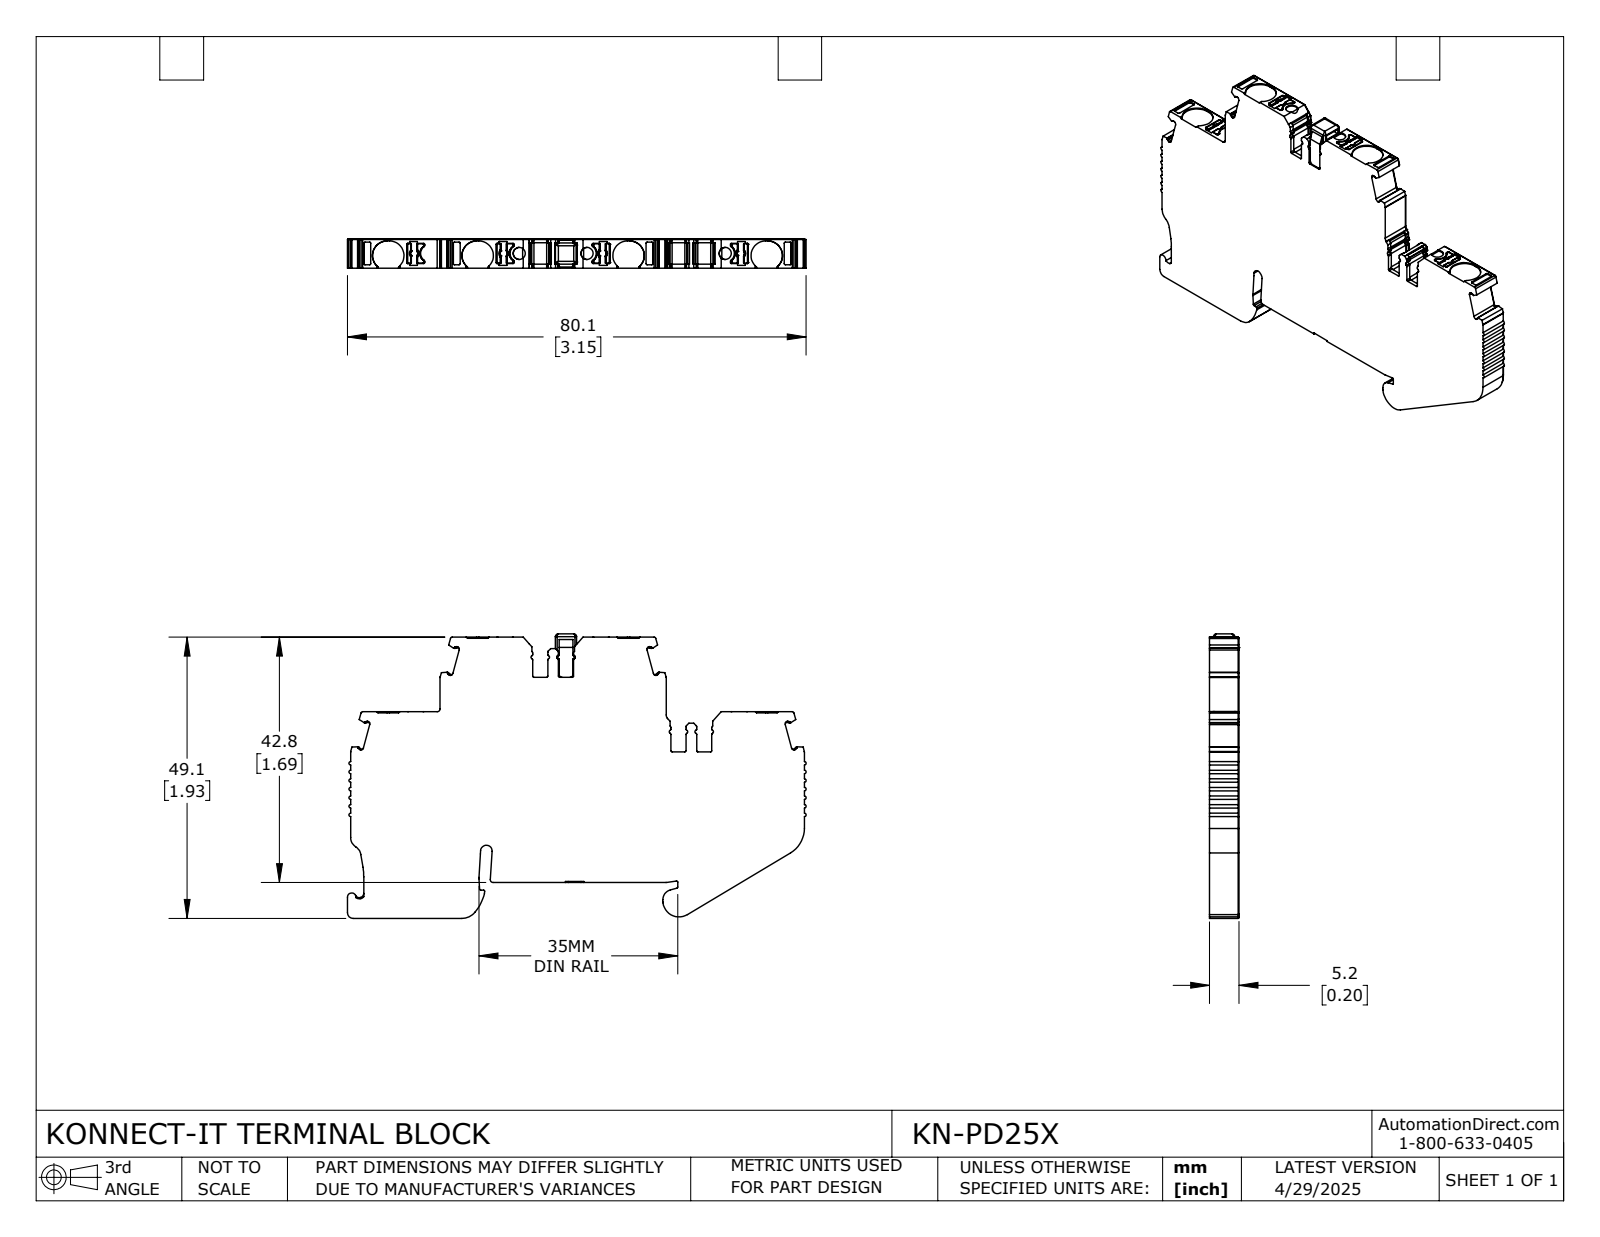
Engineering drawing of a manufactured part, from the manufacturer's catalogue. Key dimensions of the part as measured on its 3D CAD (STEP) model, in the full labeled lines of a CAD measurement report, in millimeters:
Part name (STEP PRODUCT): KN-PD25X
STEP written by: SolidWorks 2024 (CONFIG_CONTROL_DESIGN)
Units: millimetres
Bodies: 1 solid, 1081 faces (529 planar, 475 cylindrical, 77 other)
Overall size (bounding box): 80.1 × 49.7 × 5.2
Volume: 14 700 mm³ · Surface area: 7 600 mm²
Round holes (diameter × count): ⌀2.1 ×3
Partial cylindrical surfaces — rounded edges, fillets, slot ends (radius × count): R0.2 ×104, R0.3 ×61, R0.1 ×41, R0.5 ×29, R0.4 ×17, R0.2 ×16, R0.6 ×9, R0.2 ×8
Main face-to-face distances: 5.2, 13, 6.2, 42.6, 2, 29.6, 48.9, 35.9, 12.8, 36.1
Hole centre spacings: 11.8, 24.1, 36
